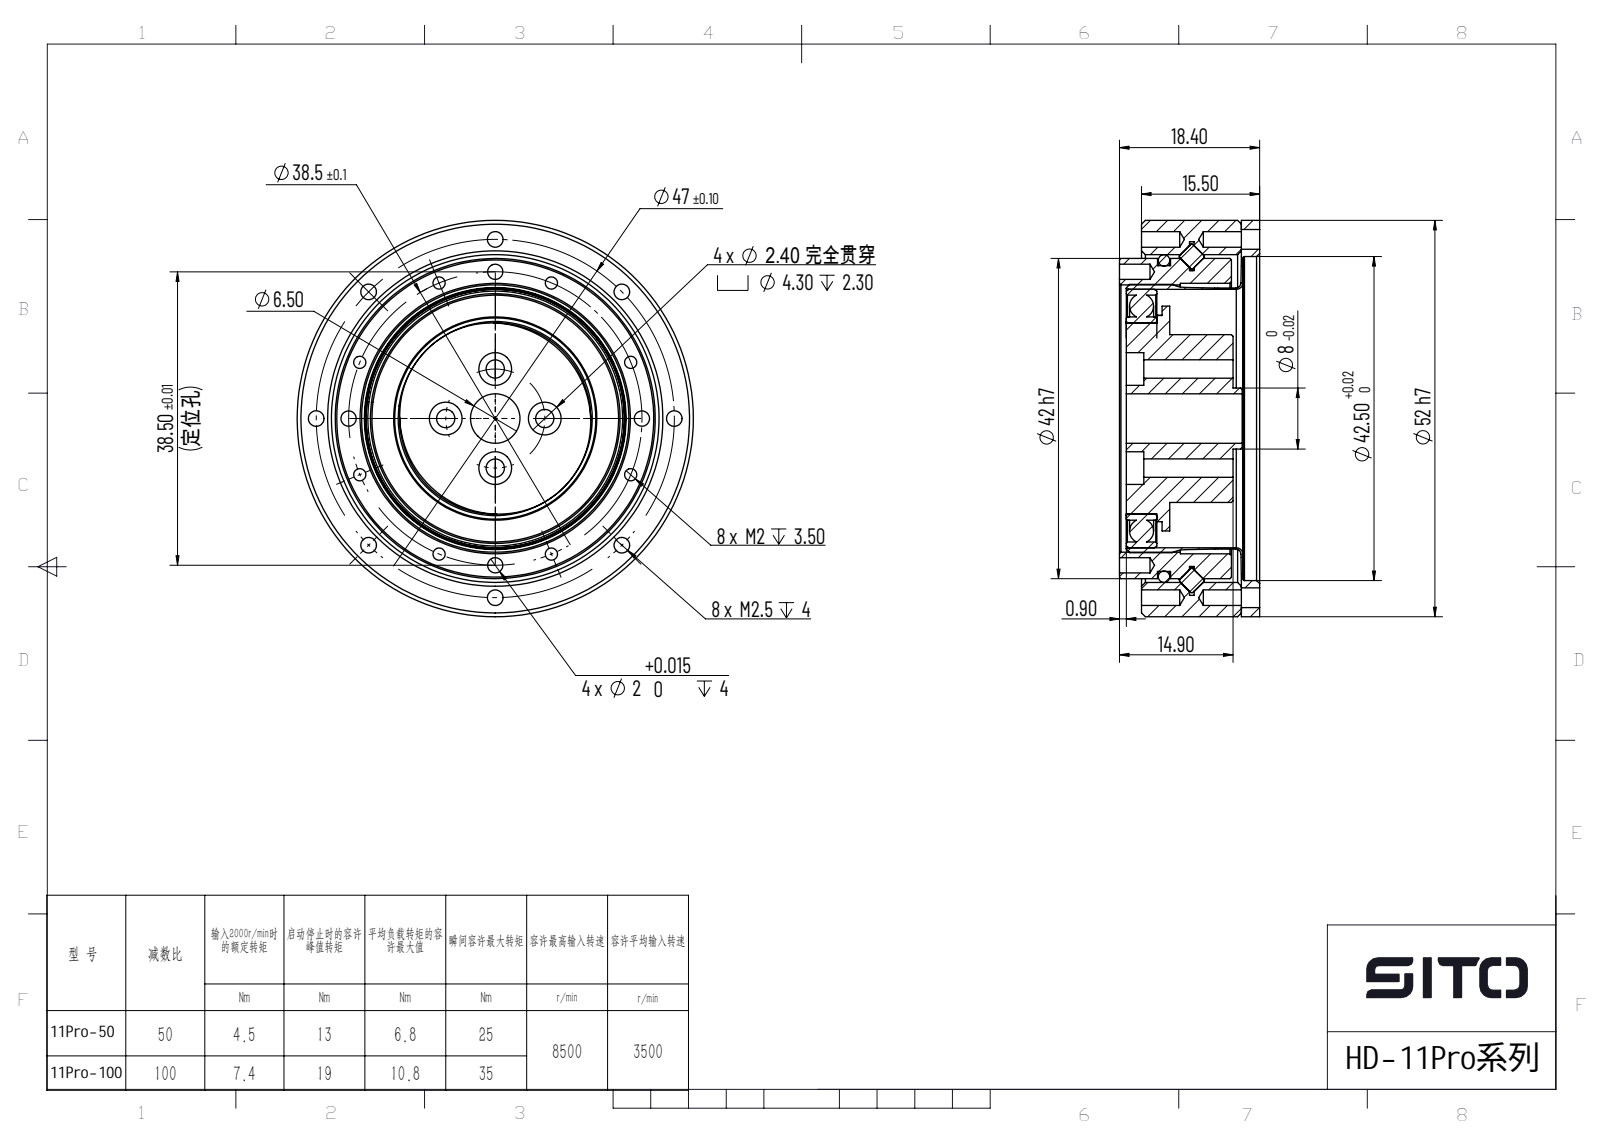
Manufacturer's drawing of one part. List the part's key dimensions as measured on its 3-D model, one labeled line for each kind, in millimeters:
Part name (STEP PRODUCT): HD-11Pro-xxx; HD-11Pro_003; HD-11Pro???? <1>; HD-11Pro_005_?? (+8 more)
STEP written by: ONSHAPE BY PTC INC, 1.201 (AP242_MANAGED_MODEL_BASED_3D_ENGINEERING_MIM_LF)
Units: millimetres
Bodies: 56 solids, 454 faces (149 planar, 126 cylindrical, 179 other)
Overall size (bounding box): 52 × 52 × 18.4
Volume: 23 246 mm³ · Surface area: 24 707 mm²
Round holes (diameter × count): ⌀1.6 ×8, ⌀2.05 ×8, ⌀2.6 ×8, ⌀2 ×4, ⌀2.4 ×4, ⌀4.3 ×4, ⌀1.25 ×1, ⌀1.8 ×1, ⌀3.3 ×1, ⌀6.5 ×1, ⌀25.07 ×1, ⌀32.37 ×1
Round bosses / shafts (diameter × count): ⌀2.5 ×48, ⌀52 ×1, ⌀42 ×1, ⌀40.1 ×1, ⌀38.8 ×1, ⌀35.21 ×1, ⌀34.25 ×1, ⌀29.5 ×1
Main face-to-face distances: 2.4, 3.7, 11.8, 2, 15.5, 13.1, 17.5, 15.1, 5.7, 8.3
Hole centre spacings: 35.62, 19.25, 27.22, 7.52, 9.32, 9.33, 13.47, 16.83
